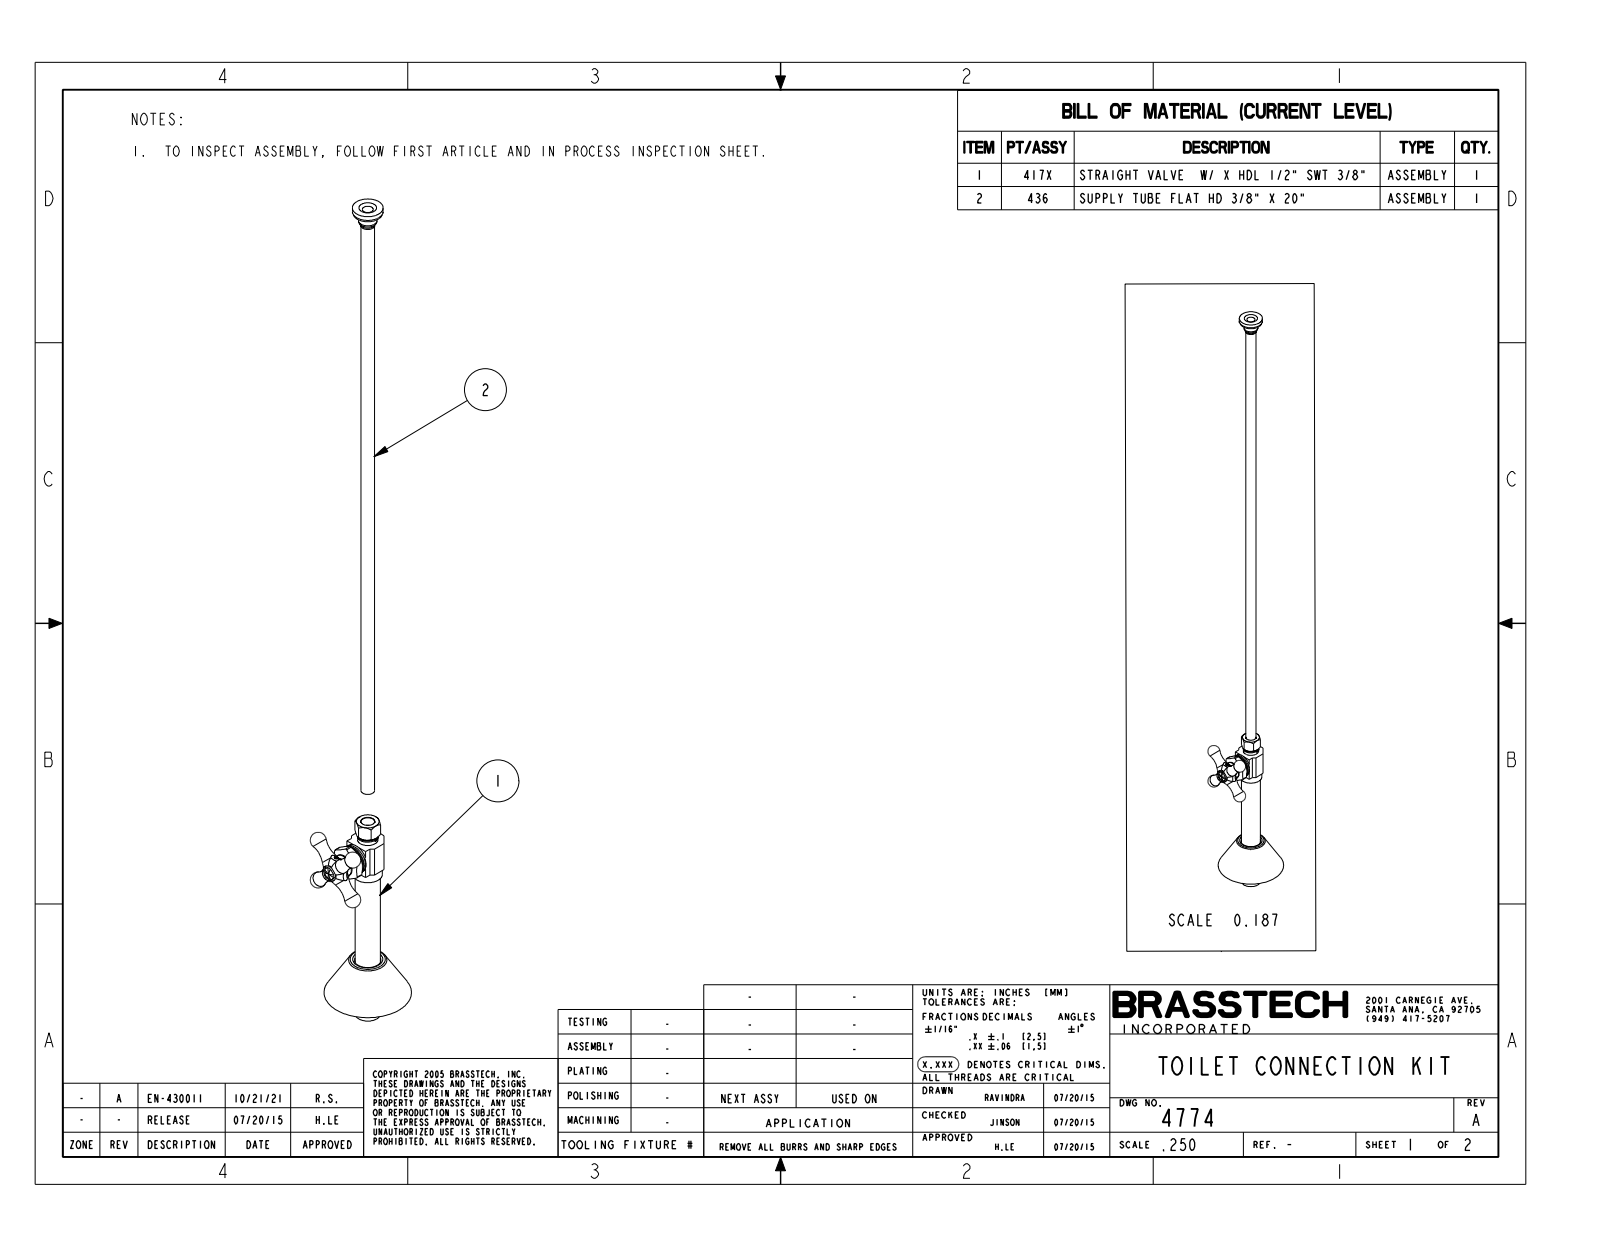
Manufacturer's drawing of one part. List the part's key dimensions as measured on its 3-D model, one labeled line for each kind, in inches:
Part name (STEP PRODUCT): 50686; 50359; 50677; 50685 (+8 more)
STEP written by: CREO PARAMETRIC BY PTC INC, 2018400 (AUTOMOTIVE_DESIGN)
Units: inches
Bodies: 12 solids, 662 faces (226 planar, 232 cylindrical, 204 other)
Overall size (bounding box): 25.345 × 2.723 × 2.4
Volume: 2.311 in³ · Surface area: 109.2 in²
Round holes (diameter × count): ⌀0.13 ×1, ⌀0.175 ×1, ⌀0.285 ×1, ⌀0.3 ×1, ⌀0.335 ×1, ⌀0.368 ×1, ⌀0.376 ×1, ⌀0.38 ×1, ⌀0.382 ×1, ⌀0.386 ×1, ⌀0.388 ×1, ⌀0.39 ×1
Round bosses / shafts (diameter × count): ⌀0.86 ×1, ⌀0.845 ×1, ⌀0.818 ×1, ⌀0.803 ×1, ⌀0.8 ×1, ⌀0.753 ×1, ⌀0.68 ×1, ⌀0.629 ×1
Partial cylindrical surfaces — rounded edges, fillets, slot ends (radius × count): R0.01 ×18, R0.05 ×6, R0.17 ×1, R0.186 ×1, R0.187 ×1
Main face-to-face distances: 0.125, 0.895, 19.353, 0.06, 0.625, 0.806, 19.478, 0.76, 0.045, 0.62
Hole centre spacings: 0.213, 1.187, 1.4
